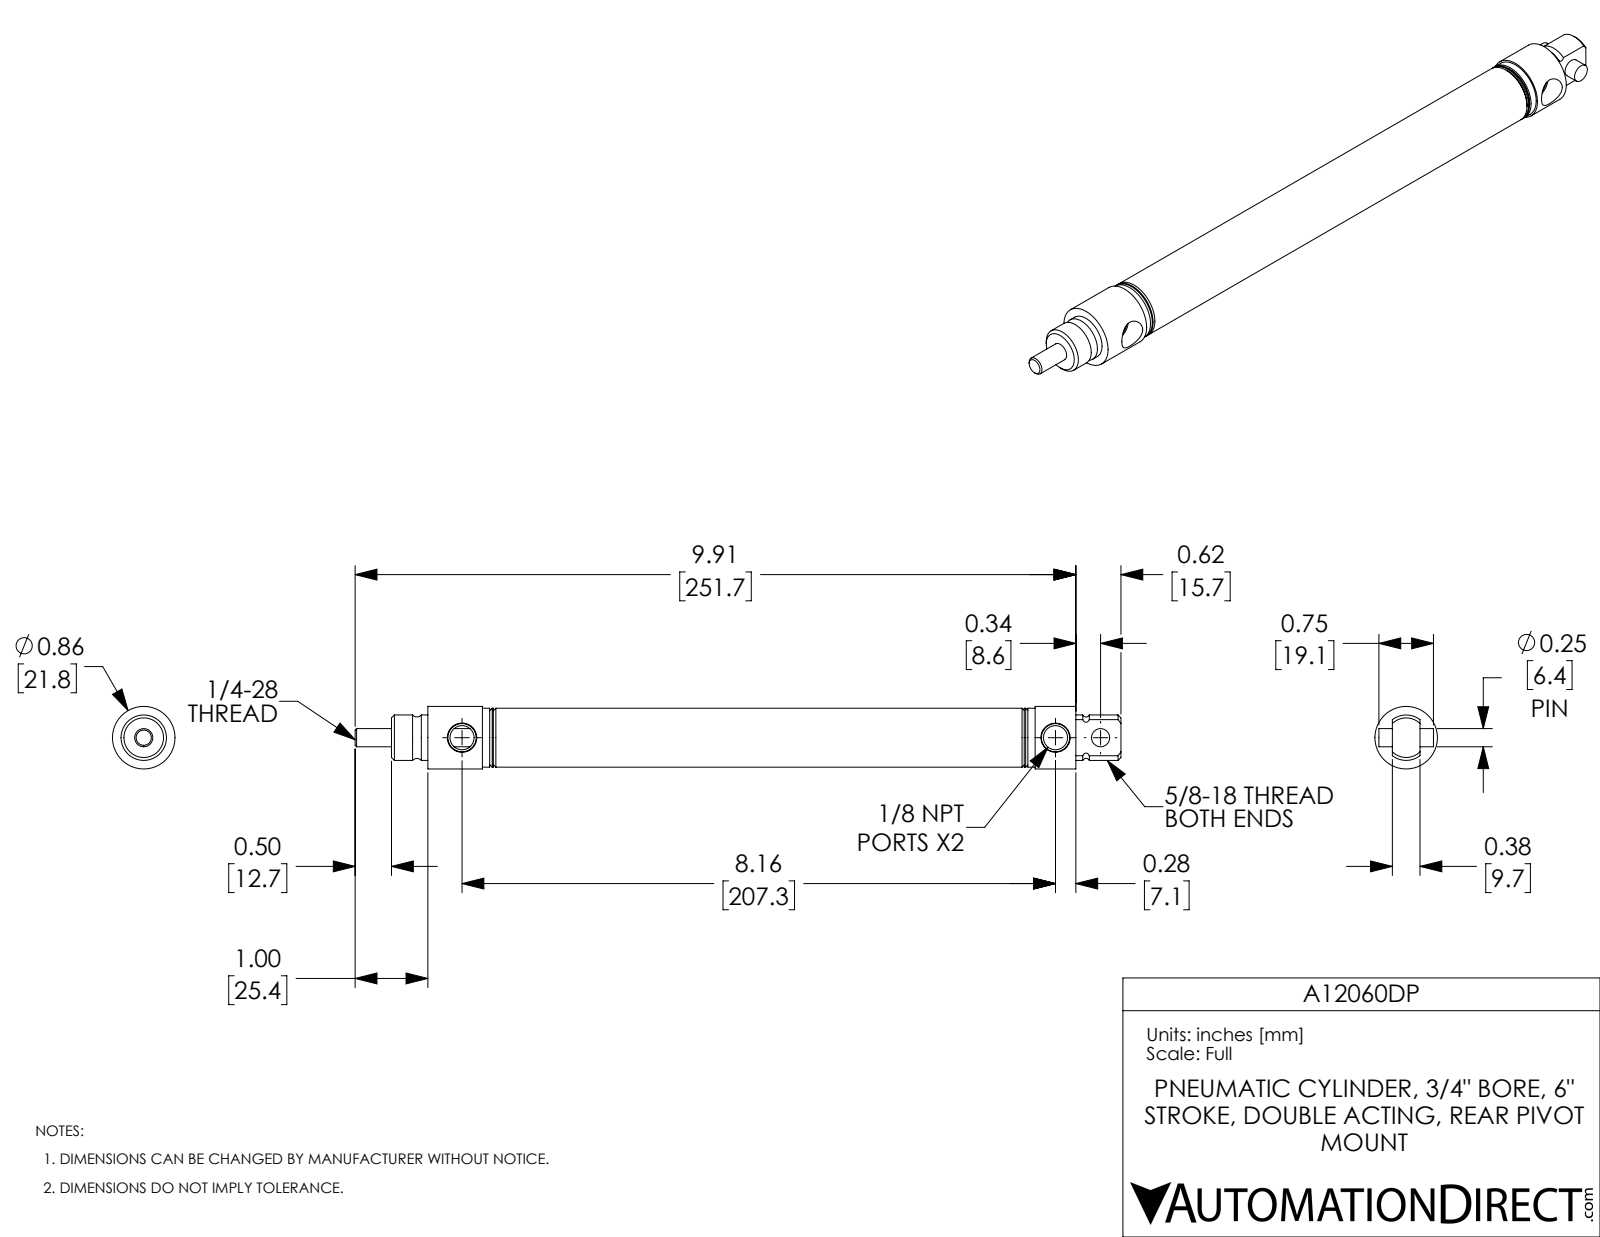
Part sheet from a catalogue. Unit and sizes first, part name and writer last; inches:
Units: inches
Overall size (bounding box): 10.53 × 0.86 × 0.86
Round holes (diameter × count): ⌀0.25 ×2, ⌀0.332 ×2, ⌀0.75 ×1
Round bosses / shafts (diameter × count): ⌀0.86 ×1, ⌀0.81 ×1, ⌀0.625 ×1
Main face-to-face distances: 0.5, 7.705, 6.5, 6, 1.205, 1.705, 7.705, 8.91, 7.205, 1.205
Hole centre spacings: 0.62, 8.16, 8.78
Volume: 2.552 in³ · Surface area: 54.21 in²
Bodies: 3 solids, 91 faces (21 planar, 38 cylindrical, 32 other)
Part name (STEP PRODUCT): A12060DP; A12060DP-PIN; A12060DP-Rod; A12060DP-MainBody
STEP written by: SolidWorks 2017 (AUTOMOTIVE_DESIGN)
